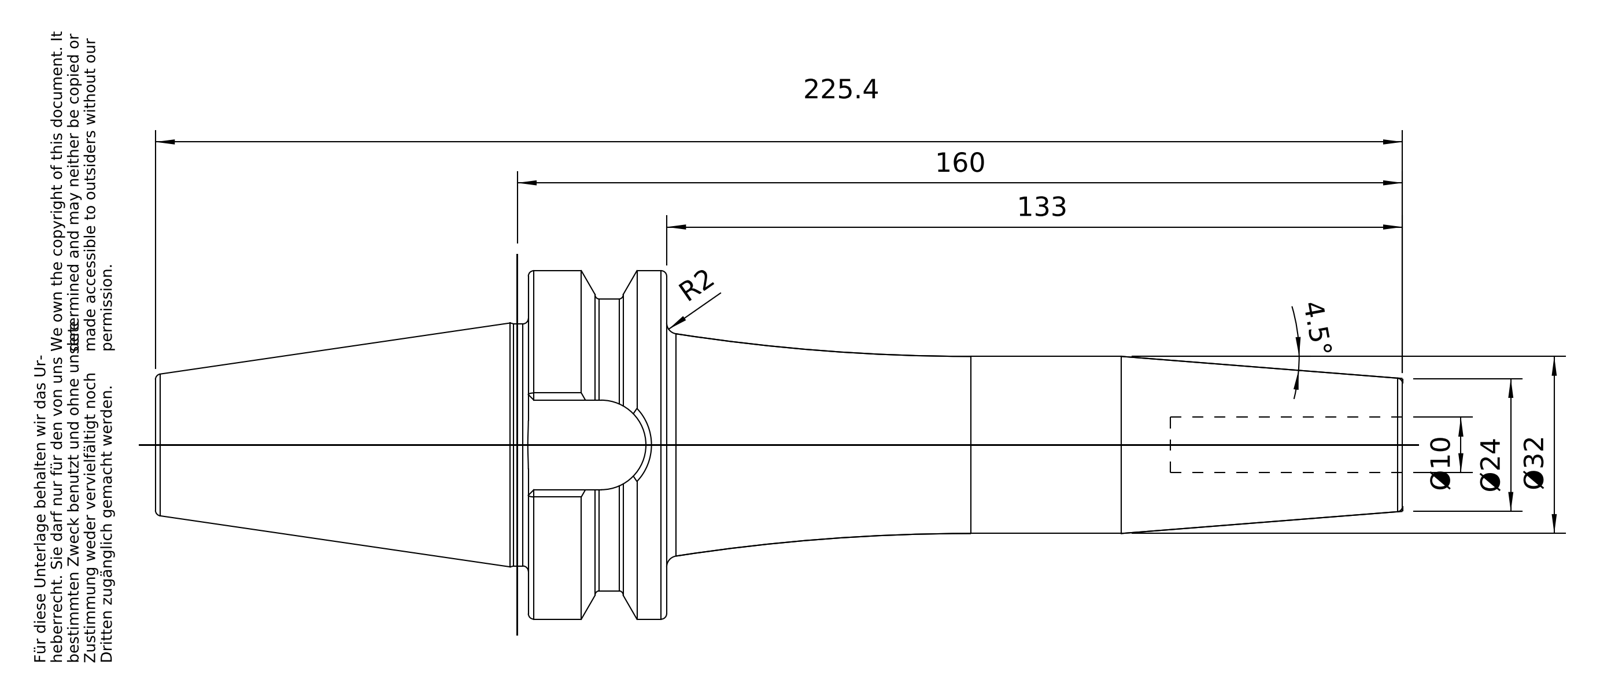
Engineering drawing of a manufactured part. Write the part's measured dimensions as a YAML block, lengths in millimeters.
part_name: "40-642-10"
step_written_by: "PRO/ENGINEER BY PARAMETRIC TECHNOLOGY CORPORATION, 2010430 (CONFIG_CONTROL_DESIGN)"
units: millimeters
bodies: {solids: 1, faces: 98, planar: 26, cylindrical: 22, other: 50}
overall_size: [225.4, 62.98, 62.98]
volume: 229150
surface_area: 35475
round_holes:
  - {diameter: 10, count: 1}
  - {diameter: 13.84, count: 1}
  - {diameter: 17.01, count: 1}
  - {diameter: 17.5, count: 1}
round_bosses_or_shafts:
  - {diameter: 62.98, count: 1}
  - {diameter: 52.75, count: 1}
  - {diameter: 43.75, count: 1}
  - {diameter: 32, count: 1}
  - {diameter: 16.01, count: 1}
partial_cylinders:
  - {radius: 8.1, count: 1}
face_to_face_distances: [25, 44.9, 158, 133, 16.2, 67.4, 92.4, 225.4, 183.4, 116]
